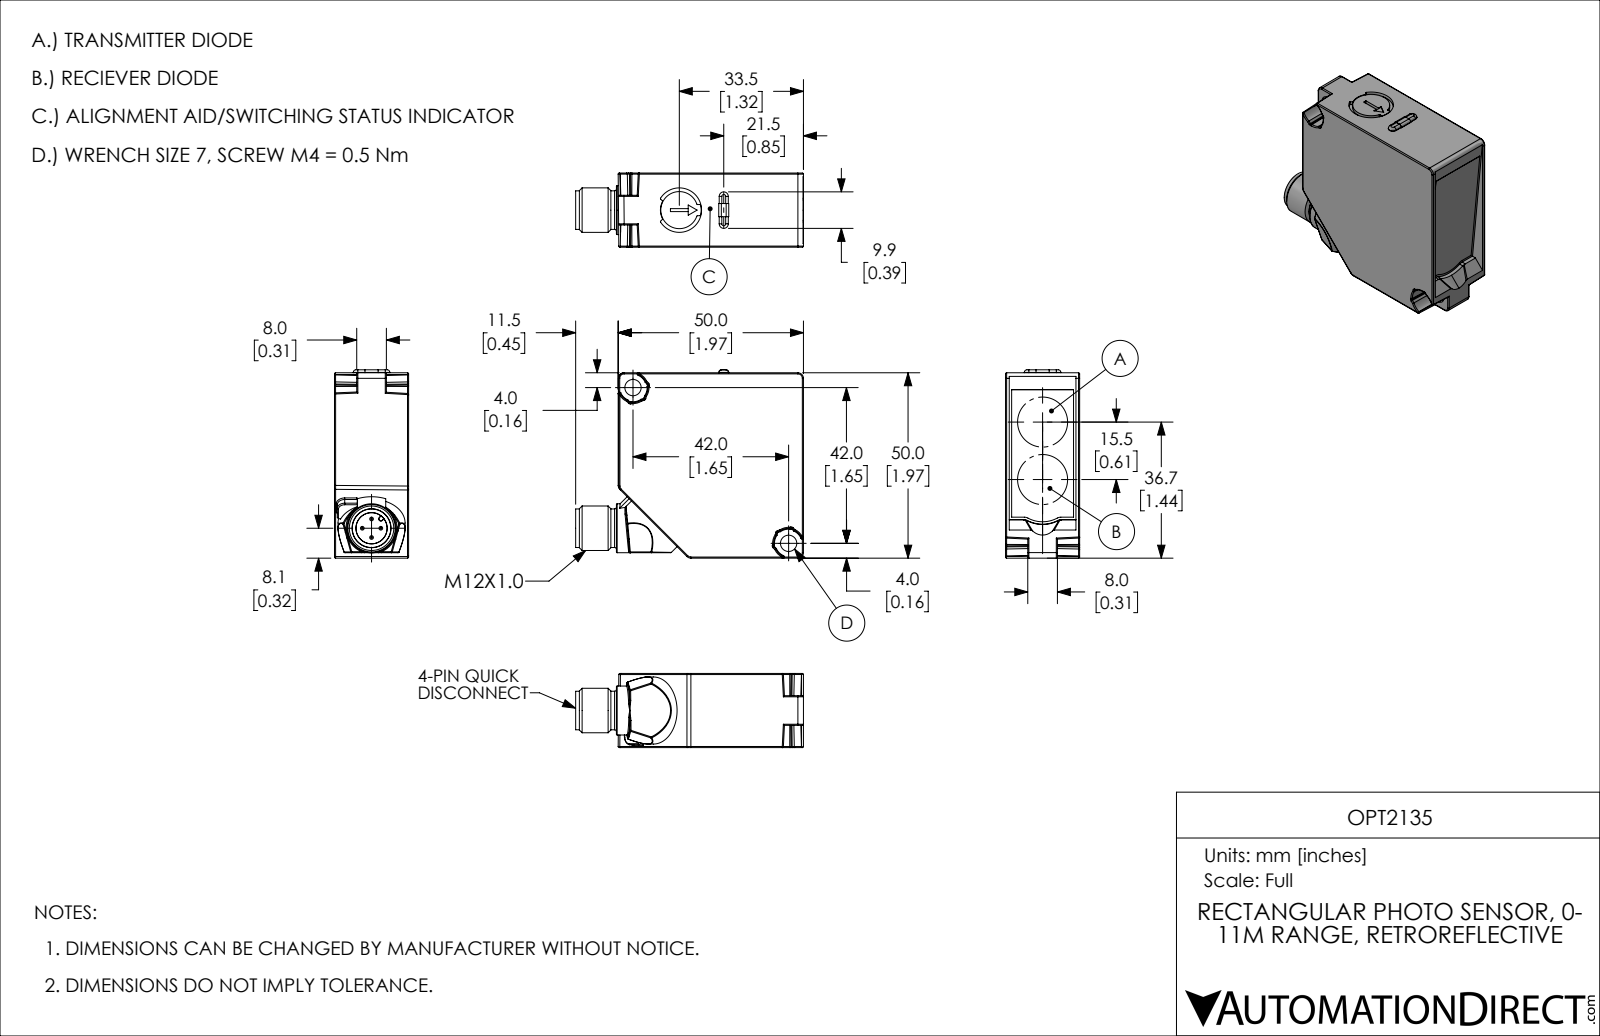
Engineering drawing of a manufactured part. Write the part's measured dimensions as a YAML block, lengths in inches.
part_name: "OPT2135"
step_written_by: "SolidWorks 2019 (AUTOMOTIVE_DESIGN)"
units: inches
bodies: {solids: 2, faces: 342, planar: 110, cylindrical: 119, other: 113}
overall_size: [2.42, 2, 0.787]
volume: 2.816
surface_area: 16.5
round_holes:
  - {diameter: 0.173, count: 2}
  - {diameter: 0.472, count: 1}
  - {diameter: 0.713, count: 1}
round_bosses_or_shafts:
  - {diameter: 0.039, count: 4}
  - {diameter: 0.52, count: 1}
  - {diameter: 0.472, count: 1}
  - {diameter: 0.409, count: 1}
  - {diameter: 0.394, count: 1}
partial_cylinders:
  - {radius: 0.012, count: 63}
  - {radius: 0.008, count: 8}
  - {radius: 0.059, count: 5}
  - {radius: 0.079, count: 5}
  - {radius: 0.028, count: 4}
  - {radius: 0.048, count: 2}
  - {radius: 0.201, count: 1}
  - {radius: 0.232, count: 1}
face_to_face_distances: [0.787, 1.969, 0.039, 0.748, 0.236, 0.551, 0.197, 0.512, 0.058, 1.911]
hole_center_spacings: [2.339]
